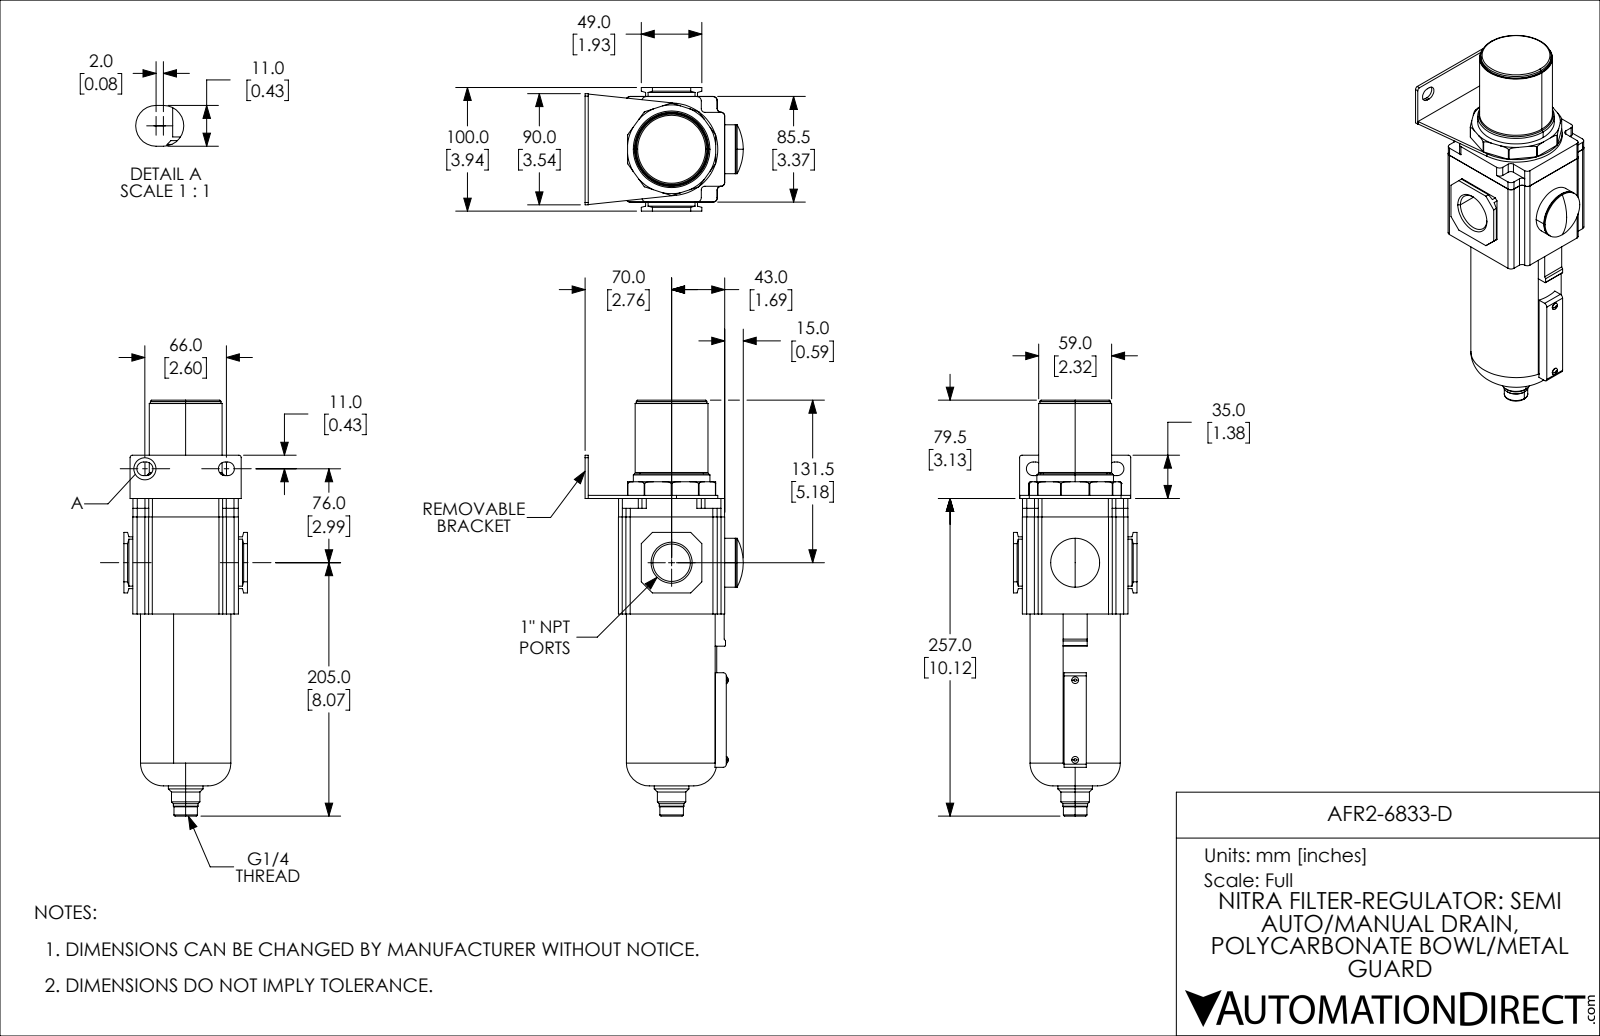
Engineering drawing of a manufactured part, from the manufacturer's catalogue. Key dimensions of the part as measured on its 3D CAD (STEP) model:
Part name (STEP PRODUCT): AFR2-6833-D
STEP written by: SolidWorks 2019 (CONFIG_CONTROL_DESIGN)
Units: millimetres
Bodies: 1 solid, 235 faces (116 planar, 79 cylindrical, 40 other)
Overall size (bounding box): 336.5 × 128 × 100
Volume: 1 494 000 mm³ · Surface area: 118 095 mm²
Round holes (diameter × count): ⌀11.45 ×1, ⌀30.29 ×1
Round bosses / shafts (diameter × count): ⌀5.5 ×2, ⌀73.1 ×1, ⌀62 ×1, ⌀59 ×1, ⌀57 ×1, ⌀51.4 ×1, ⌀39.6 ×1, ⌀28 ×1
Partial cylindrical surfaces — rounded edges, fillets, slot ends (radius × count): R3 ×20, R3.5 ×12, R5.5 ×4, R2 ×2, R2.5 ×2, R37.4 ×1
Main face-to-face distances: 2.5, 85.5, 86, 110.5, 27, 113, 7.25, 92.75, 93.5, 96
